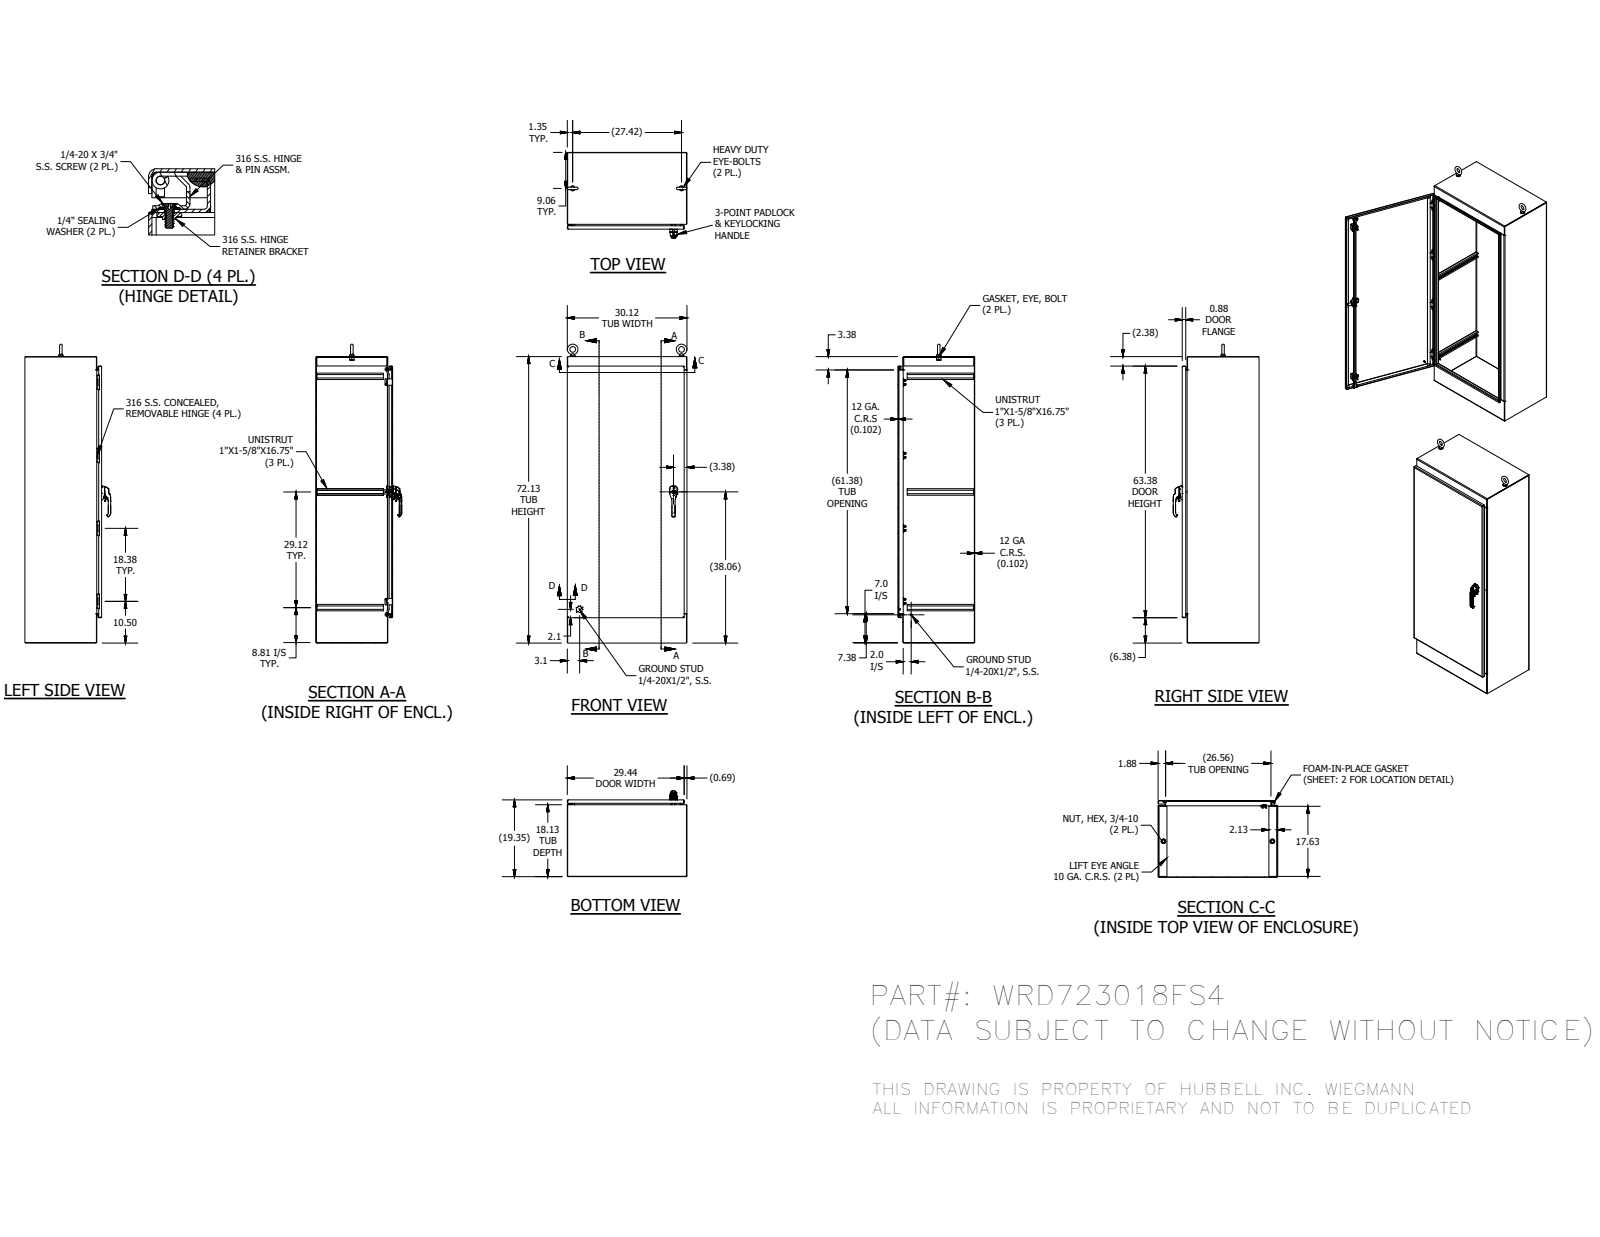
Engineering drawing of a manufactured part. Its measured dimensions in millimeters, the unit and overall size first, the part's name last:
Units: millimetres
Overall size (bounding box): 1911.29 × 765.23 × 549.04
Round holes (diameter × count): ⌀5.84 ×8, ⌀7.02 ×8, ⌀7.14 ×8, ⌀16.51 ×8, ⌀5.08 ×4, ⌀5.4 ×3, ⌀6 ×3, ⌀7.11 ×3, ⌀6.13 ×2, ⌀6.35 ×2, ⌀6.41 ×2, ⌀10.16 ×2
Round bosses / shafts (diameter × count): ⌀6.35 ×15, ⌀15.88 ×8, ⌀10.25 ×8, ⌀4.63 ×8, ⌀31.75 ×2, ⌀28.45 ×2, ⌀25.4 ×2, ⌀19.05 ×2
Partial cylindrical surfaces — rounded edges, fillets, slot ends (radius × count): R0.5 ×164, R0.3 ×85, R1.59 ×27, R0.25 ×24, R3.17 ×20, R0.47 ×19, R2 ×15, R1.27 ×14
Main face-to-face distances: 2.59, 488.83, 762.59, 486.24, 491.42, 760, 765.18, 1829.39, 457.79, 31.04
Hole centre spacings: 12.5, 25.4, 466.73, 933.45, 6.5, 22.5, 51.5, 6
Volume: 16 700 000 mm³ · Surface area: 12 540 000 mm²
Bodies: 85 solids, 3586 faces (1457 planar, 1207 cylindrical, 922 other)
Part name (STEP PRODUCT): WRD723018FS4BLR; WRD3018FS4TOP; WRD3018FS4BTM; WRD7230FS4DR (+8 more)
STEP written by: Autodesk Inventor 2016 (AUTOMOTIVE_DESIGN)
